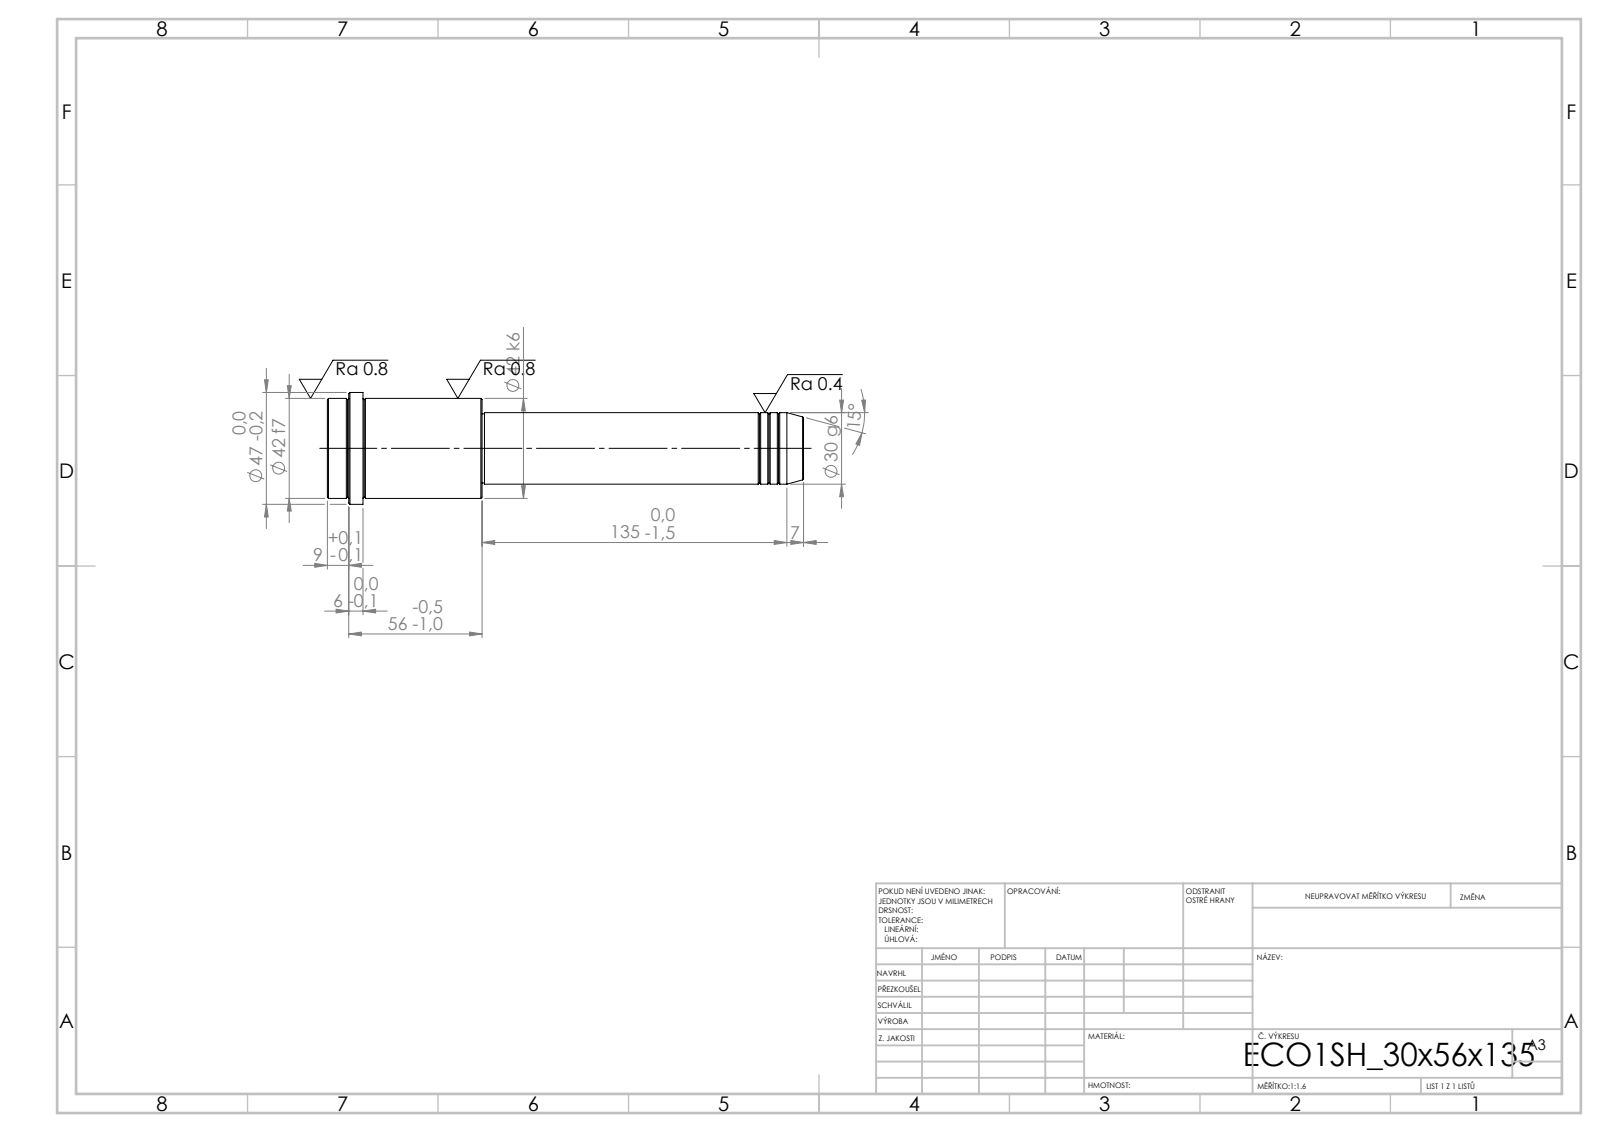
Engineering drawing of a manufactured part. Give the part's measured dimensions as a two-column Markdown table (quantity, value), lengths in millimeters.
| quantity | value |
| --- | --- |
| STEP written by | SolidWorks 2019 (CONFIG_CONTROL_DESIGN) |
| units | millimeters |
| bodies | 1 solid, 52 faces (6 planar, 16 cylindrical, 30 other) |
| overall size | 200 × 47 × 47 |
| volume | 186 672 mm³ |
| surface area | 24 934 mm² |
| round bosses / shafts (diameter × count) | 47 × 1, 42 × 1, 30 × 1, 29 × 1 |
| main face-to-face distances | 65, 135, 200, 185, 50, 15, 191, 56, 6, 9 |
